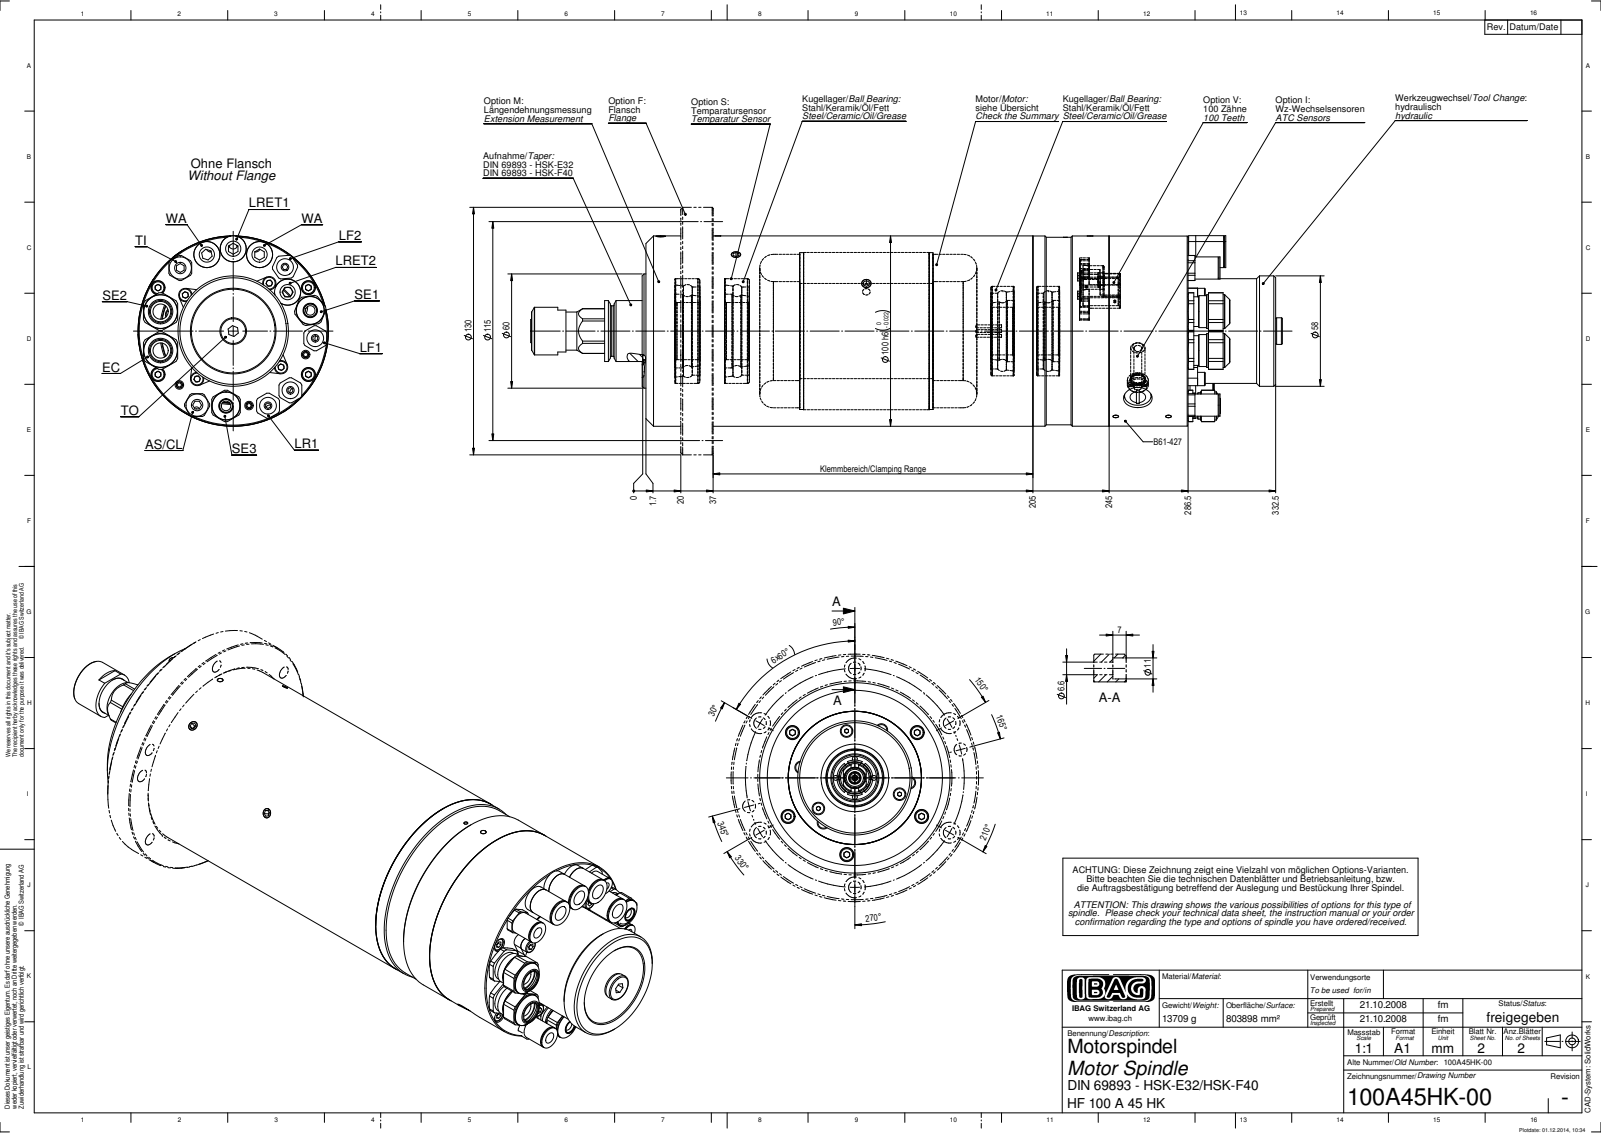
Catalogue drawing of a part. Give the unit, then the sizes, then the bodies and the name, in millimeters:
Units: millimetres
Overall size (bounding box): 394.86 × 100.1 × 100.05
Round holes (diameter × count): ⌀7.4 ×9, ⌀8 ×6, ⌀4 ×4, ⌀4.5 ×3, ⌀15 ×3, ⌀5 ×2, ⌀6 ×2, ⌀6.7 ×2, ⌀10.7 ×2, ⌀16.2 ×2, ⌀10 ×1, ⌀35.5 ×1
Round bosses / shafts (diameter × count): ⌀5.7 ×7, ⌀13.7 ×4, ⌀13.7 ×4, ⌀8.8 ×4, ⌀7 ×4, ⌀14 ×3, ⌀17.8 ×2, ⌀16.79 ×2
Partial cylindrical surfaces — rounded edges, fillets, slot ends (radius × count): R5 ×7, R6.6 ×6, R8.25 ×2, R9.9 ×2, R11.75 ×1
Main face-to-face distances: 243.3, 284.8, 41.5, 40, 203.3, 81.5, 225, 18.3, 185, 266.5
Hole centre spacings: 43.25, 45.6, 39.5, 40, 40.5, 72.27, 72.54, 5.1
Bodies: 0 solids, 871 faces (370 planar, 324 cylindrical, 177 other)
Part name (STEP PRODUCT): 100A45HK-00
STEP written by: SolidWorks 2012 (CONFIG_CONTROL_DESIGN)
